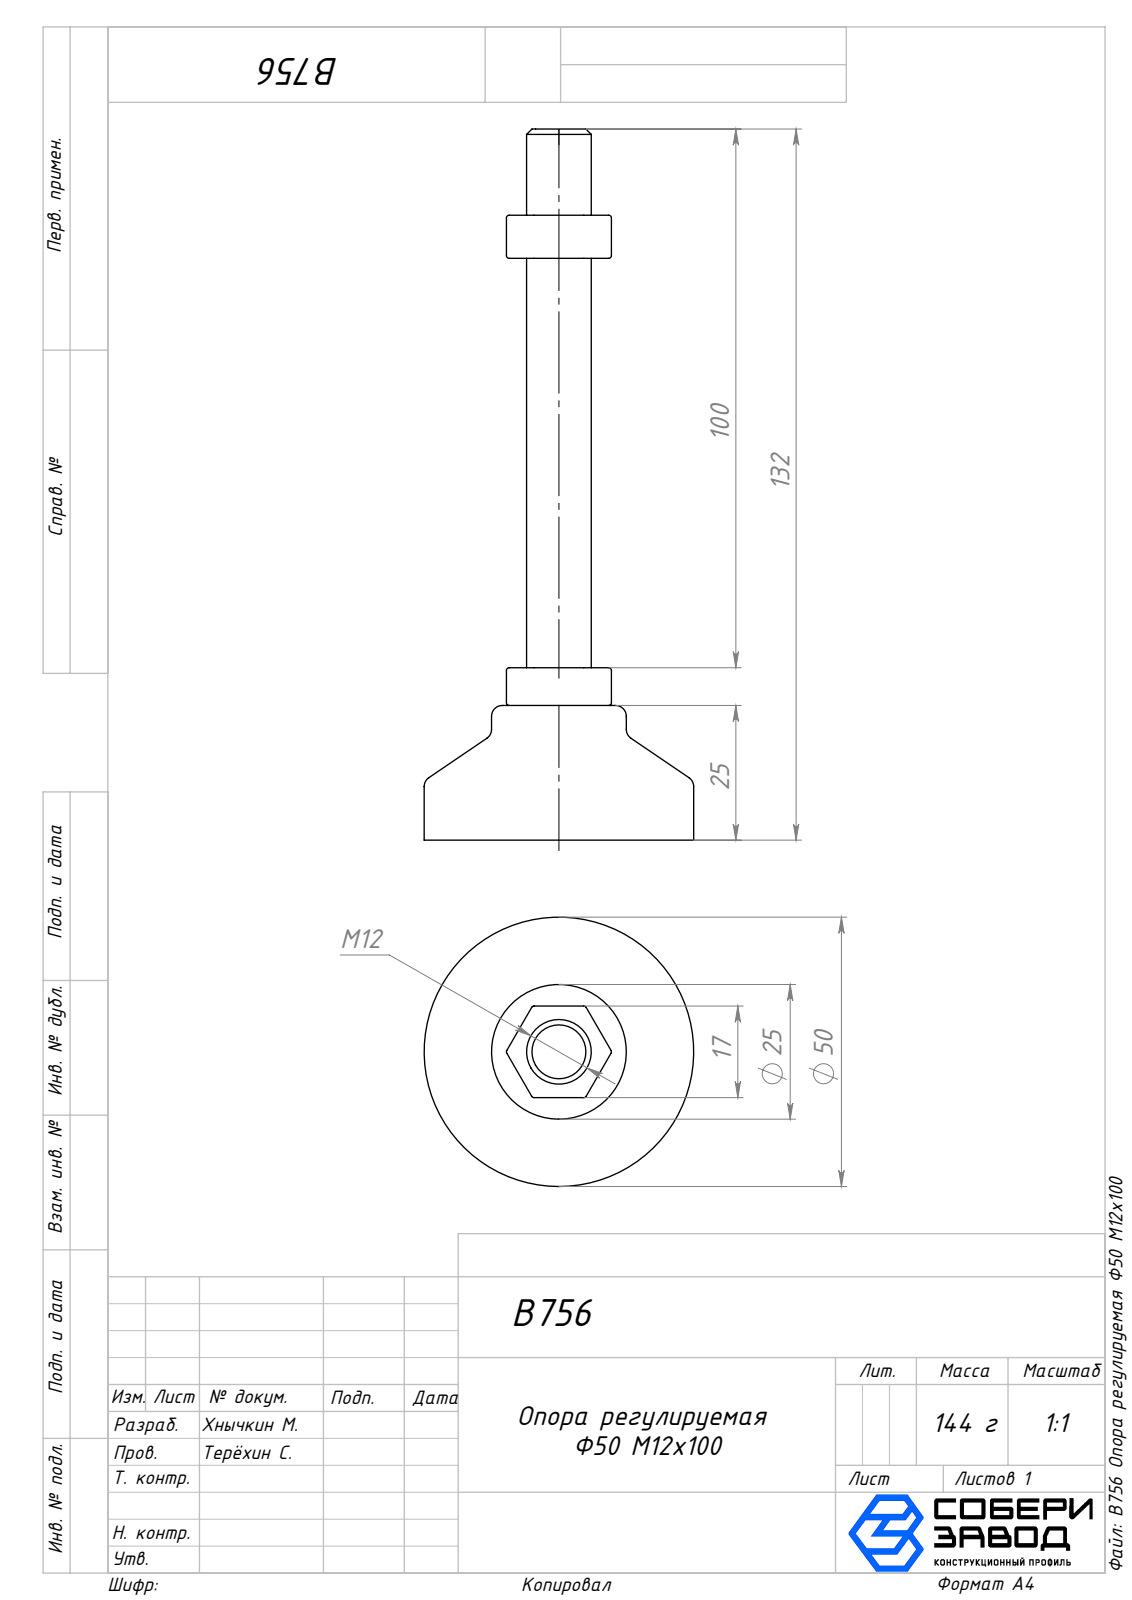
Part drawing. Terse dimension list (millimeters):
name: Опора_00; B756 Опора регулируемая Ф50 М12х100; Вал_00; Гайка_00 (+1 more)
written by: SolidWorks 2025 (AUTOMOTIVE_DESIGN)
unit: mm
bodies: 4 solids, 156 faces (29 planar, 70 cylindrical, 57 other)
size: 132 × 50 × 50
volume: 42 905 mm³; area: 13 837 mm²
holes: 1× ⌀4, 1× ⌀10, 1× ⌀27
bosses: 1× ⌀50, 1× ⌀25, 1× ⌀12, 1× ⌀5
rounds: 48× R0.5
face distances: 11, 25, 14, 17, 2, 15, 108, 97, 83, 116
